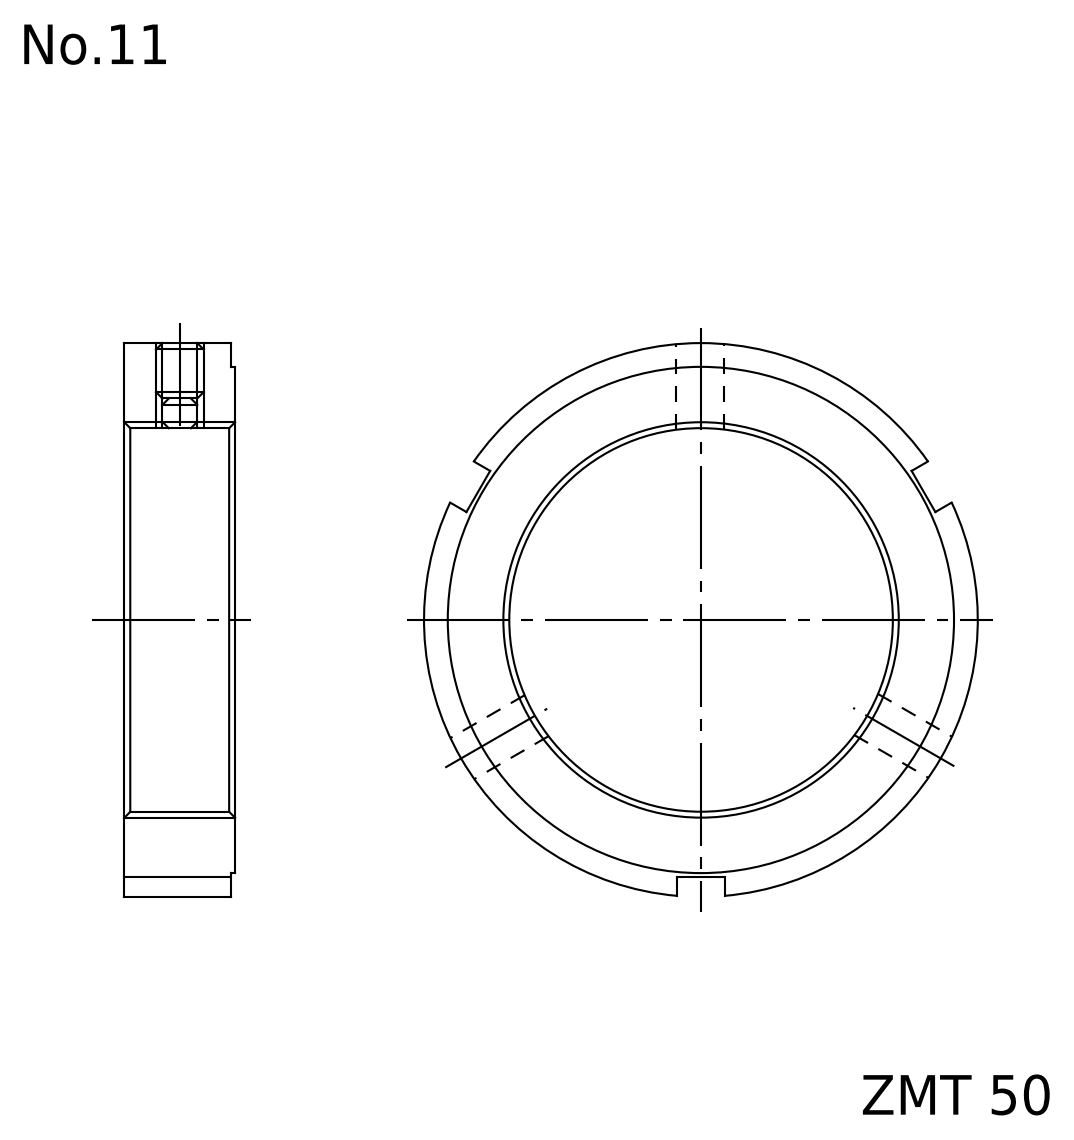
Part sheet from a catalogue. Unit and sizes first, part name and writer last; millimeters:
Units: millimetres
Overall size (bounding box): 70 × 69.87 × 14
Round holes (diameter × count): ⌀4.92 ×3, ⌀50 ×1
Round bosses / shafts (diameter × count): ⌀70 ×1, ⌀64 ×1
Main face-to-face distances: 14, 0.5, 13.5, 6
Volume: 24 907 mm³ · Surface area: 9 492 mm²
Bodies: 1 solid, 20 faces (12 planar, 8 cylindrical, 0 other)
Part name (STEP PRODUCT): FKD ZMT 50
STEP written by: Autodesk Inventor 2011 (AUTOMOTIVE_DESIGN)
